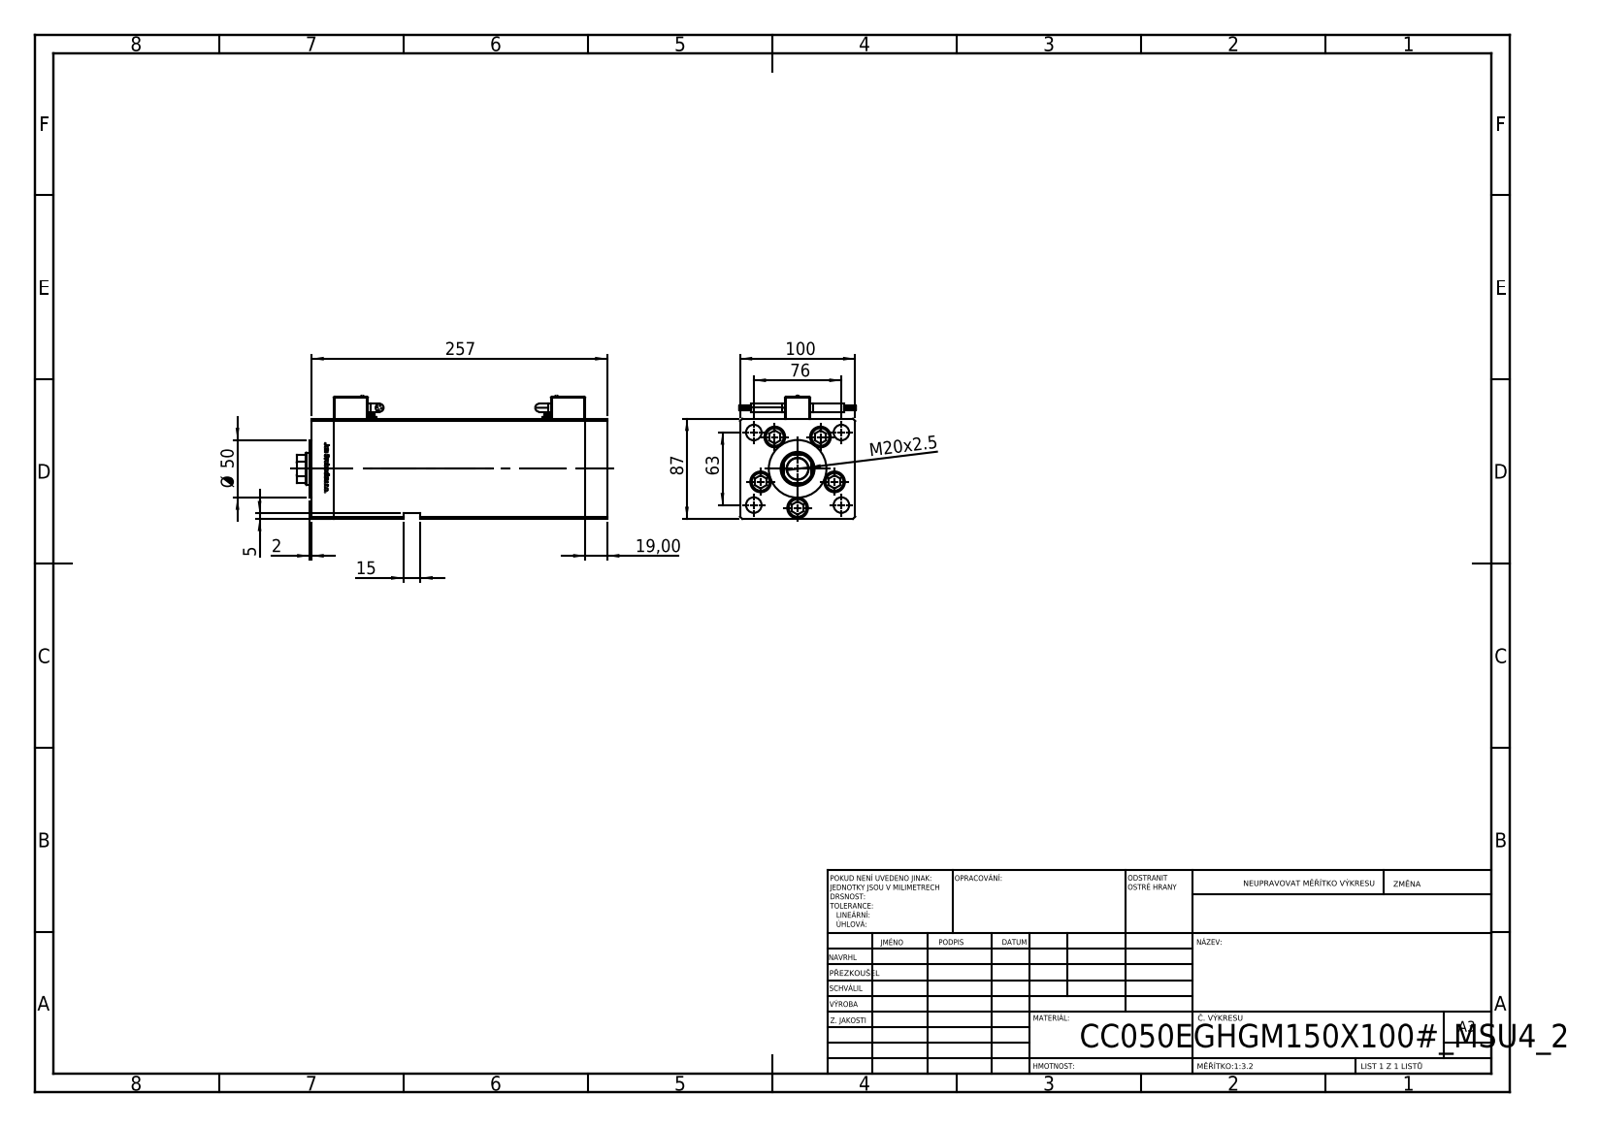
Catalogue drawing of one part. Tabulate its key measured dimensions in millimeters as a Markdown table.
| quantity | value |
| --- | --- |
| part name | V220C_VC_E; V220C BACK_E; V220C_E MIDDLE; Magnetic_Switch_MSU4 (+2 more) |
| STEP written by | SolidWorks 2019 (CONFIG_CONTROL_DESIGN) |
| units | millimeters |
| bodies | 16 solids, 1416 faces (551 planar, 255 cylindrical, 610 other) |
| overall size | 269.5 × 107.1 × 101.6 |
| volume | 1 903 000 mm³ |
| surface area | 277 112 mm² |
| round holes (diameter × count) | 13.5 × 11, 18 × 5, 18.5 × 5, 12.5 × 4, 2 × 2, 3.6 × 2, 5 × 2, 7 × 2, 13.16 × 2, 28 × 1, 29.5 × 1 |
| round bosses / shafts (diameter × count) | 0.85 × 8, 17 × 5, 8 × 5, 7 × 4, 6 × 2, 3.5 × 2, 2.5 × 2, 50 × 1 |
| partial cylindrical surfaces (radius × count) | 1 × 24, 4 × 4, 0.93 × 2, 13.5 × 1 |
| main face-to-face distances | 100, 87, 19, 218.5, 237.5, 34.25, 256.5, 6.5, 15.25, 203.25 |
| hole center spacings | 34, 18.59, 39.64, 49.36, 57.95, 8.25, 21.03, 37.5 |
